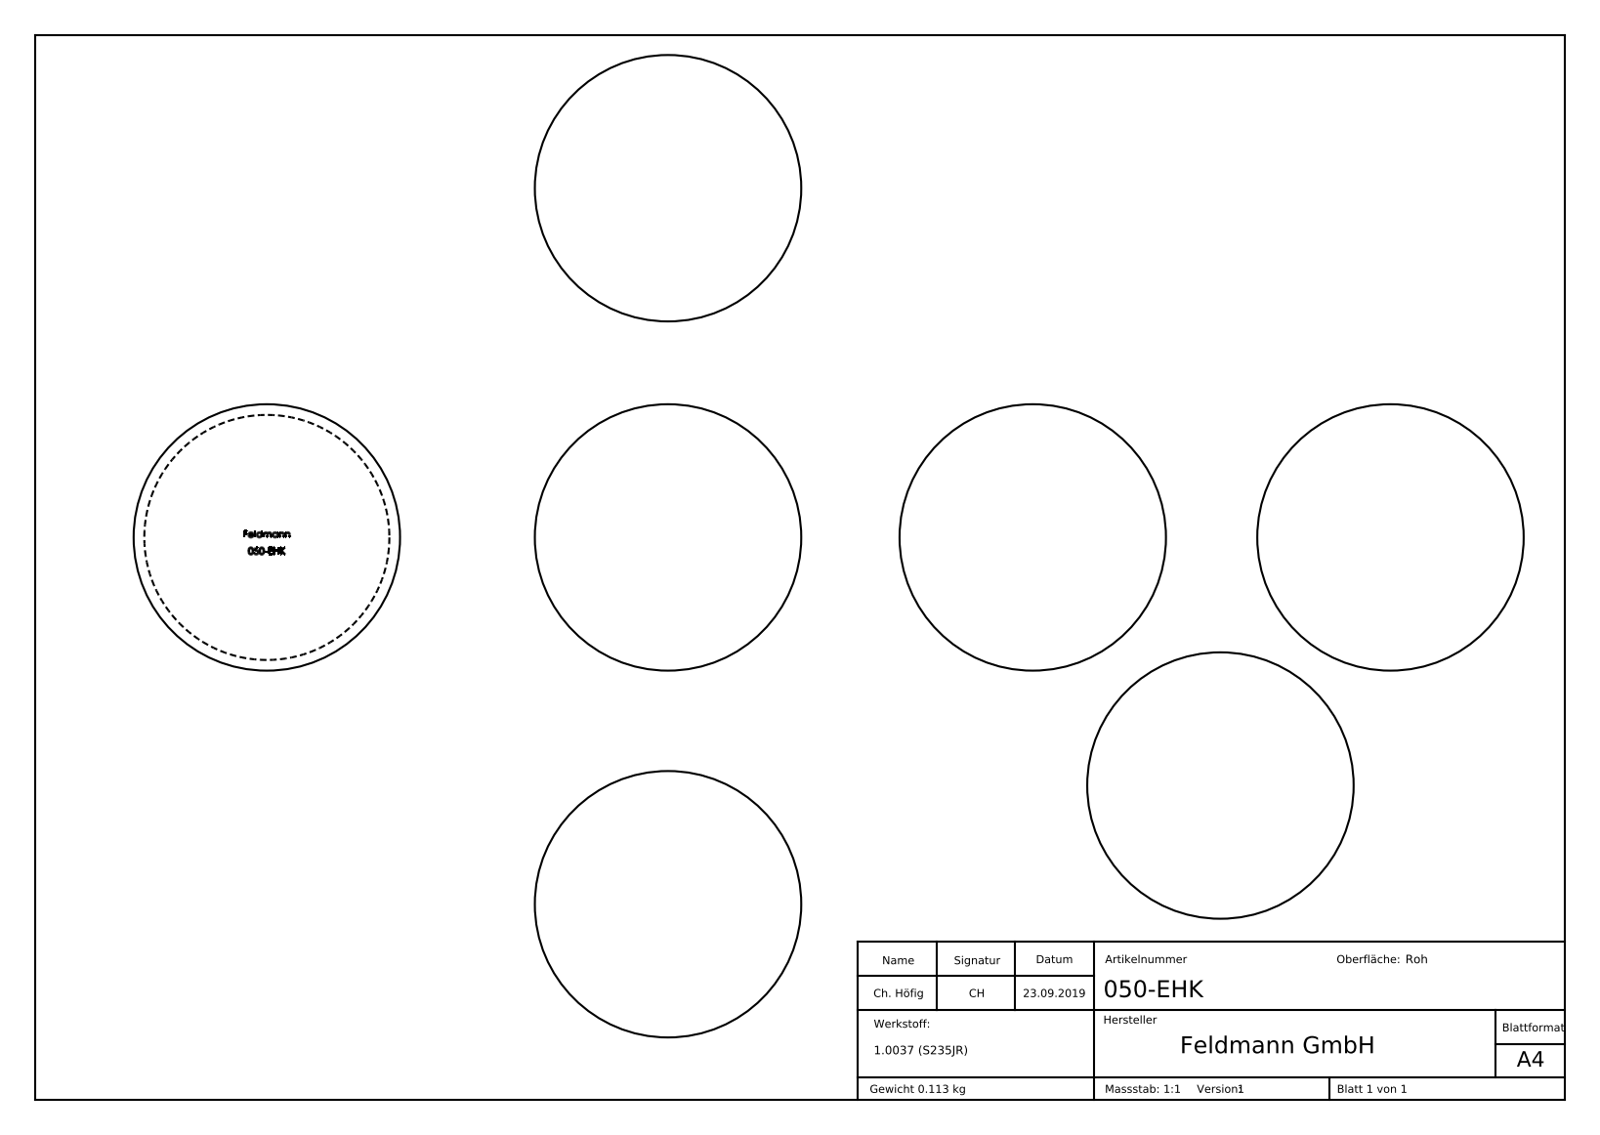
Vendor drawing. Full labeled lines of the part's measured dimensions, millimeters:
Part name (STEP PRODUCT): 050-EHK
STEP written by: SolidWorks 2015 (CONFIG_CONTROL_DESIGN)
Units: millimetres
Bodies: 1 solid, 199 faces (99 planar, 0 cylindrical, 100 other)
Overall size (bounding box): 50 × 50 × 50
Volume: 14 484 mm³ · Surface area: 14 510 mm²
Main face-to-face distances: 3.2, 1.26, 3.13, 4.5, 0.46, 1.35, 3.59, 0.68, 0.54, 0.64
